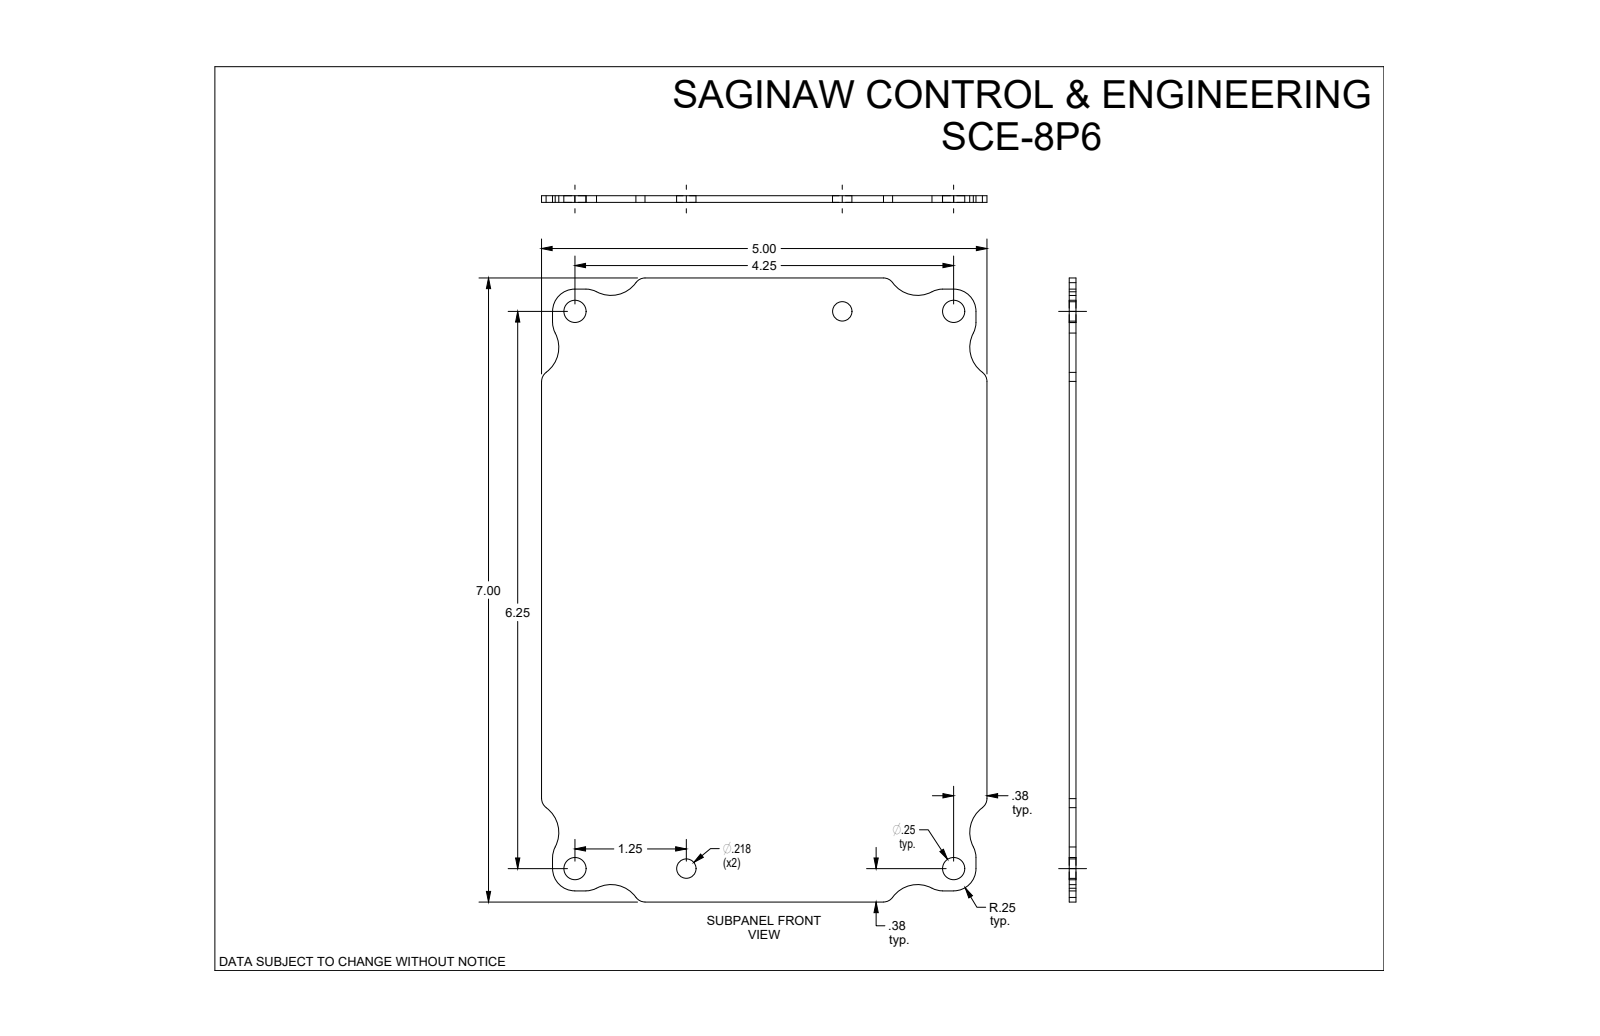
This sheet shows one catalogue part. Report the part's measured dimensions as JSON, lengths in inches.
{"part_name": "SCE-8P6", "step_written_by": "SolidWorks 2019 (CONFIG_CONTROL_DESIGN)", "units": "inches", "bodies": {"solids": 1, "faces": 48, "planar": 14, "cylindrical": 34, "other": 0}, "overall_size": [7, 5, 0.075], "volume_in3": 2.514, "surface_area_in2": 69.13, "round_holes": [[0.25, 4], [0.218, 2]], "partial_cylinders_radius": [[0.25, 12], [0.125, 8], [0.344, 8]], "face_to_face_distances": [0.075, 5, 7, 0.124, 4.876, 0.125, 6.875, 4.752, 6.75], "hole_center_spacings": [1.25, 3, 4.25, 6.25, 6.374, 6.933, 7.558, 6.491]}
